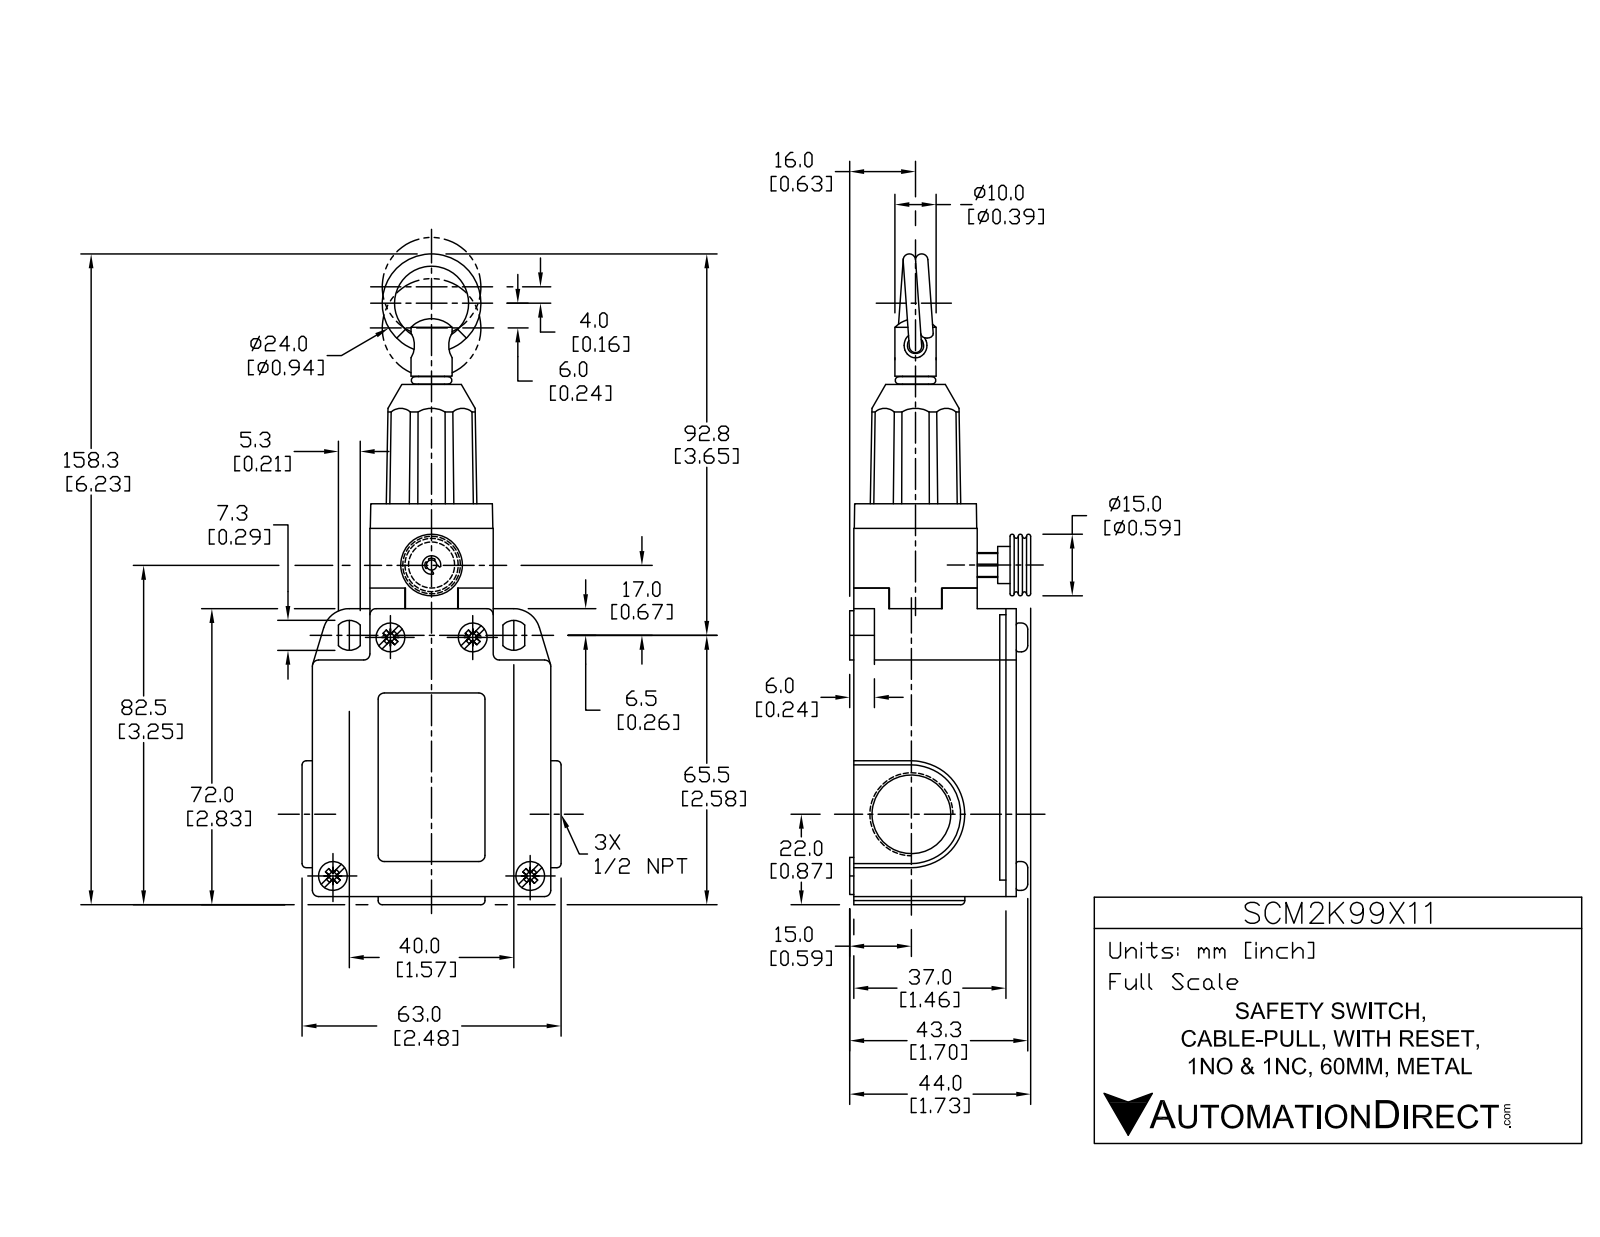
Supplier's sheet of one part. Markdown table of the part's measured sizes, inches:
| quantity | value |
| --- | --- |
| part name | SCM2K99X11 |
| STEP written by | SolidWorks 2017 (AUTOMOTIVE_DESIGN) |
| units | inches |
| bodies | 5 solids, 256 faces (100 planar, 94 cylindrical, 62 other) |
| overall size | 6.28 × 2.441 × 1.724 |
| volume | 11.03 in³ |
| surface area | 50.03 in² |
| round holes (diameter × count) | 0.669 × 2, 0.748 × 2, 0.157 × 1, 0.398 × 1, 0.709 × 1 |
| round bosses / shafts (diameter × count) | 0.276 × 4, 0.472 × 2, 0.354 × 2, 0.701 × 1, 0.394 × 1, 0.386 × 1, 0.264 × 1, 0.248 × 1 |
| partial cylindrical surfaces (radius × count) | 0.059 × 12, 0.144 × 2, 0.256 × 2, 0.512 × 2, 0.453 × 1, 0.472 × 1 |
| main face-to-face distances | 1.555, 0.551, 1.732, 1.181, 2.283, 0.079, 0.236, 0.157, 0.197, 2.756 |
| hole center spacings | 0.039, 4.528 |
